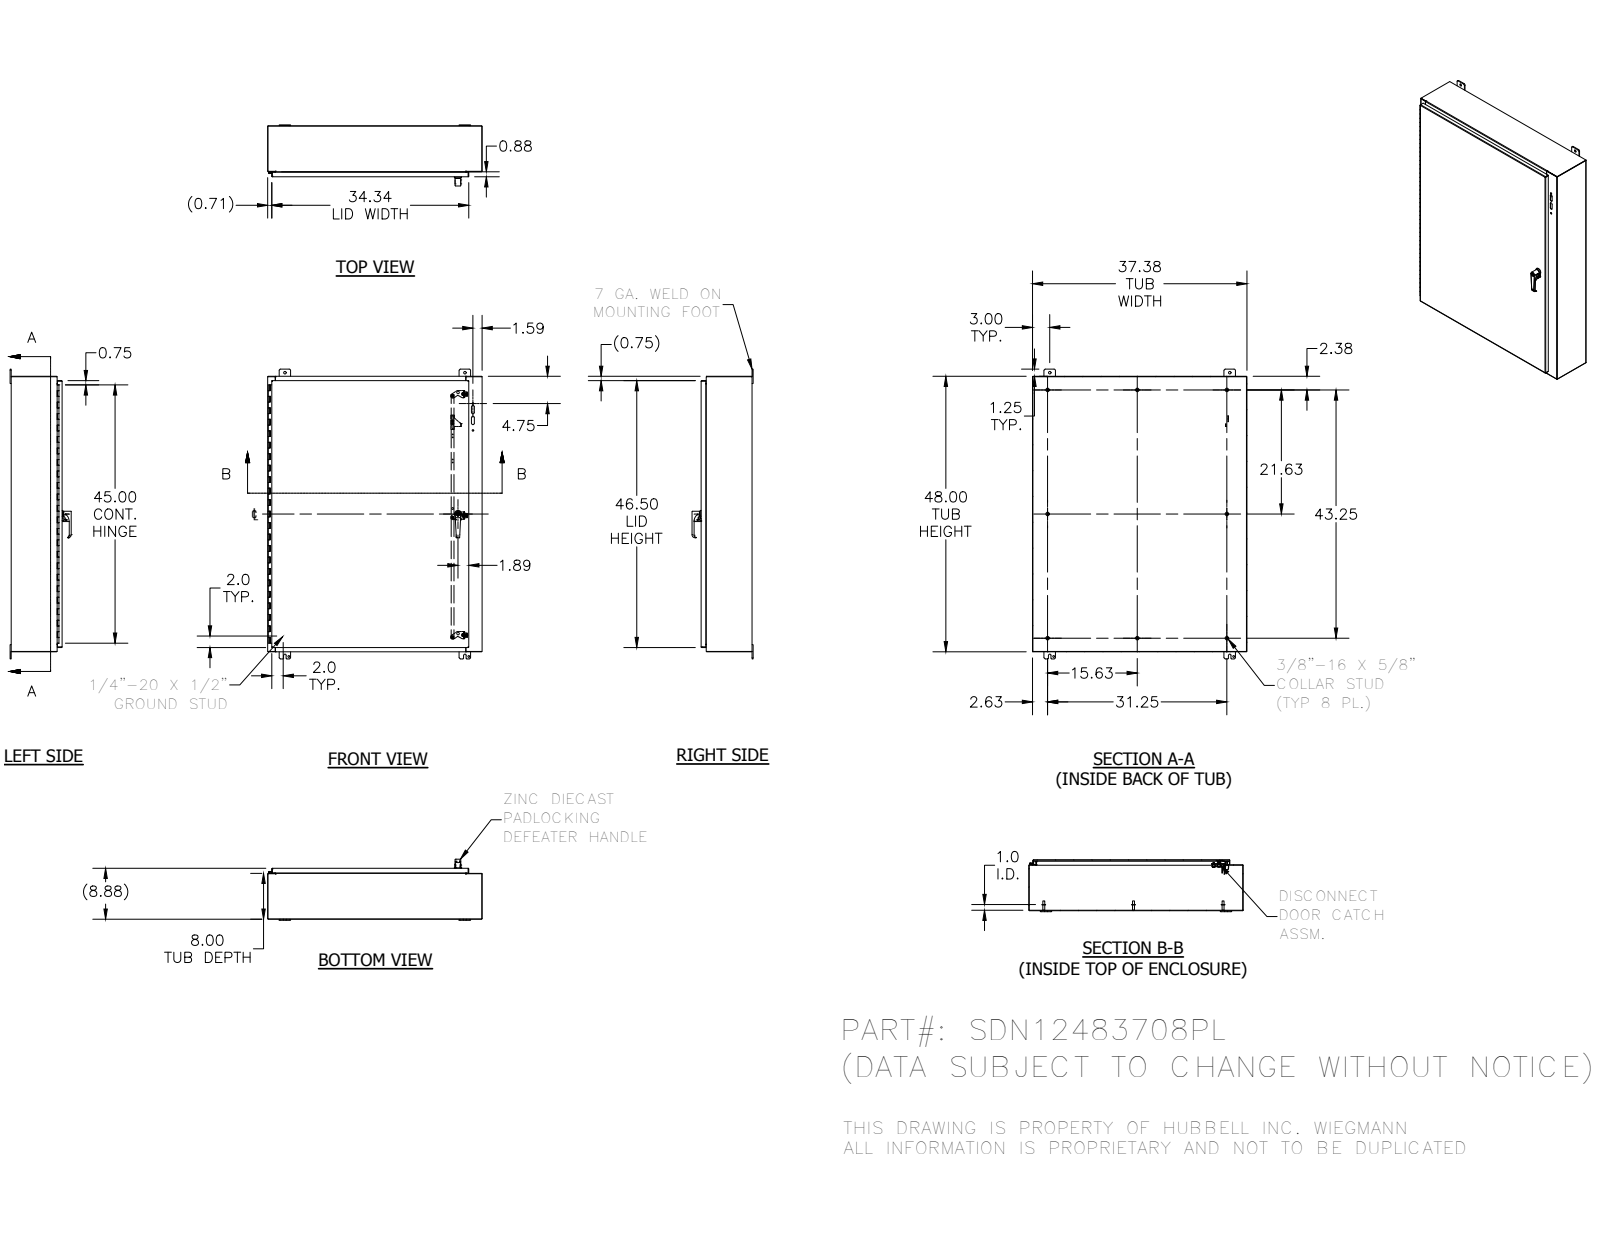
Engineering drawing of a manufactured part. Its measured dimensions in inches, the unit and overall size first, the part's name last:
Units: inches
Overall size (bounding box): 50.5 × 37.375 × 10.649
Round holes (diameter × count): ⌀0.145 ×6, ⌀0.313 ×4, ⌀0.32 ×4, ⌀0.438 ×4, ⌀0.196 ×3, ⌀0.211 ×3, ⌀0.22 ×3, ⌀0.313 ×3, ⌀0.45 ×3, ⌀0.156 ×2, ⌀0.281 ×2, ⌀0.307 ×2
Round bosses / shafts (diameter × count): ⌀0.625 ×10, ⌀0.33 ×10, ⌀0.437 ×6, ⌀0.3 ×6, ⌀0.225 ×6, ⌀0.25 ×4, ⌀0.19 ×4, ⌀0.75 ×3
Partial cylindrical surfaces — rounded edges, fillets, slot ends (radius × count): R0.02 ×38, R0.012 ×31, R0.025 ×24, R0.25 ×23, R0.031 ×18, R0.105 ×18, R0.125 ×18, R0.094 ×6
Main face-to-face distances: 0.074, 8.801, 8.727, 8.875, 37.301, 47.926, 7.926, 0.875, 37.227, 37.375
Hole centre spacings: 20.844, 21.156, 42, 1.593, 31.375, 48, 57.344, 0.5
Volume: 408.9 in³ · Surface area: 10 967 in²
Bodies: 64 solids, 1889 faces (1012 planar, 623 cylindrical, 254 other)
Part name (STEP PRODUCT): SDN12483708PL; SDN12483708PLBLR; 3889; 34840 (+8 more)
STEP written by: Autodesk Inventor 2012 (AUTOMOTIVE_DESIGN)
